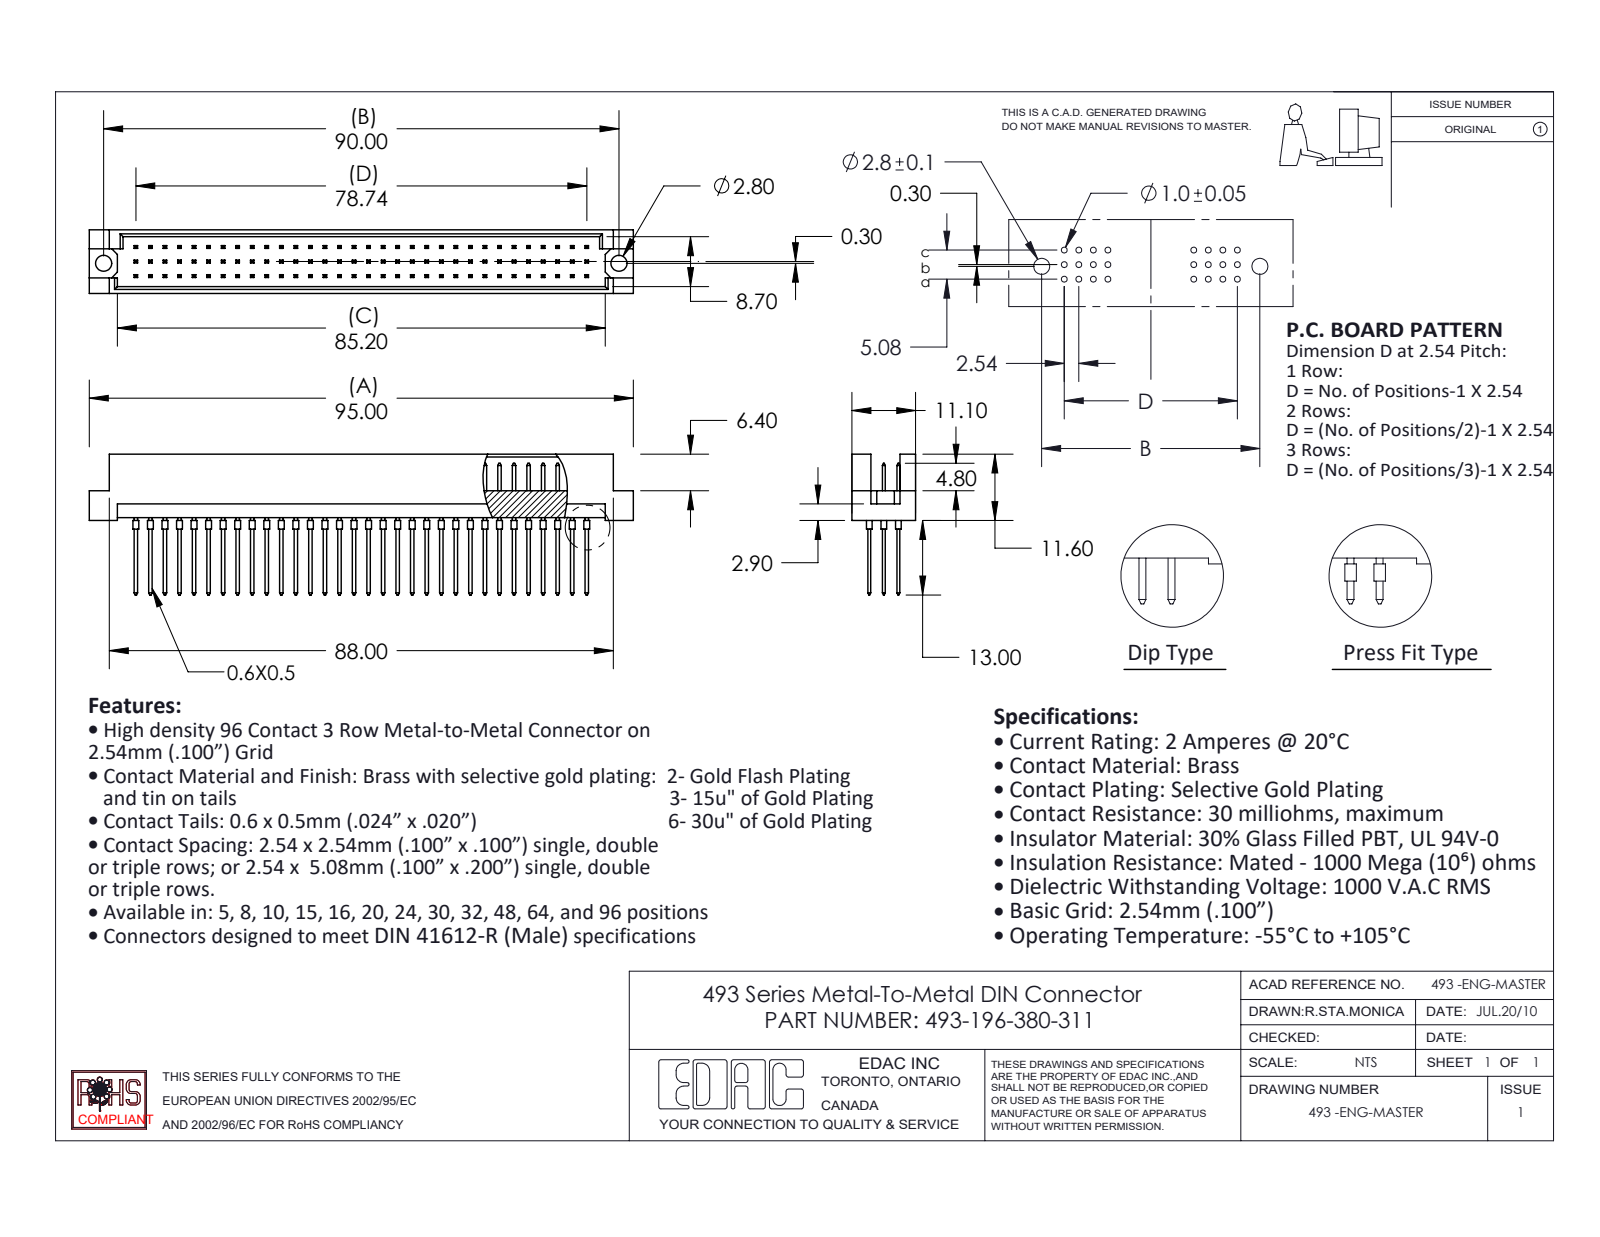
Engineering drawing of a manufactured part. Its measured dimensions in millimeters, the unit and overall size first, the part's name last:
Units: millimetres
Overall size (bounding box): 95 × 24.6 × 11.1
Round holes (diameter × count): ⌀2.8 ×2
Round bosses / shafts (diameter × count): ⌀1 ×96
Main face-to-face distances: 2.54, 0.5, 5.08, 1.2, 9.9, 2.76, 3.26, 5.3, 5.8, 7.84
Hole centre spacings: 90
Volume: 6 380 mm³ · Surface area: 11 523 mm²
Bodies: 97 solids, 2548 faces (2352 planar, 196 cylindrical, 0 other)
Part name (STEP PRODUCT): 493-196-380-311; 493 Part_96; 493-290_80
STEP written by: SolidWorks 2020 (CONFIG_CONTROL_DESIGN)
